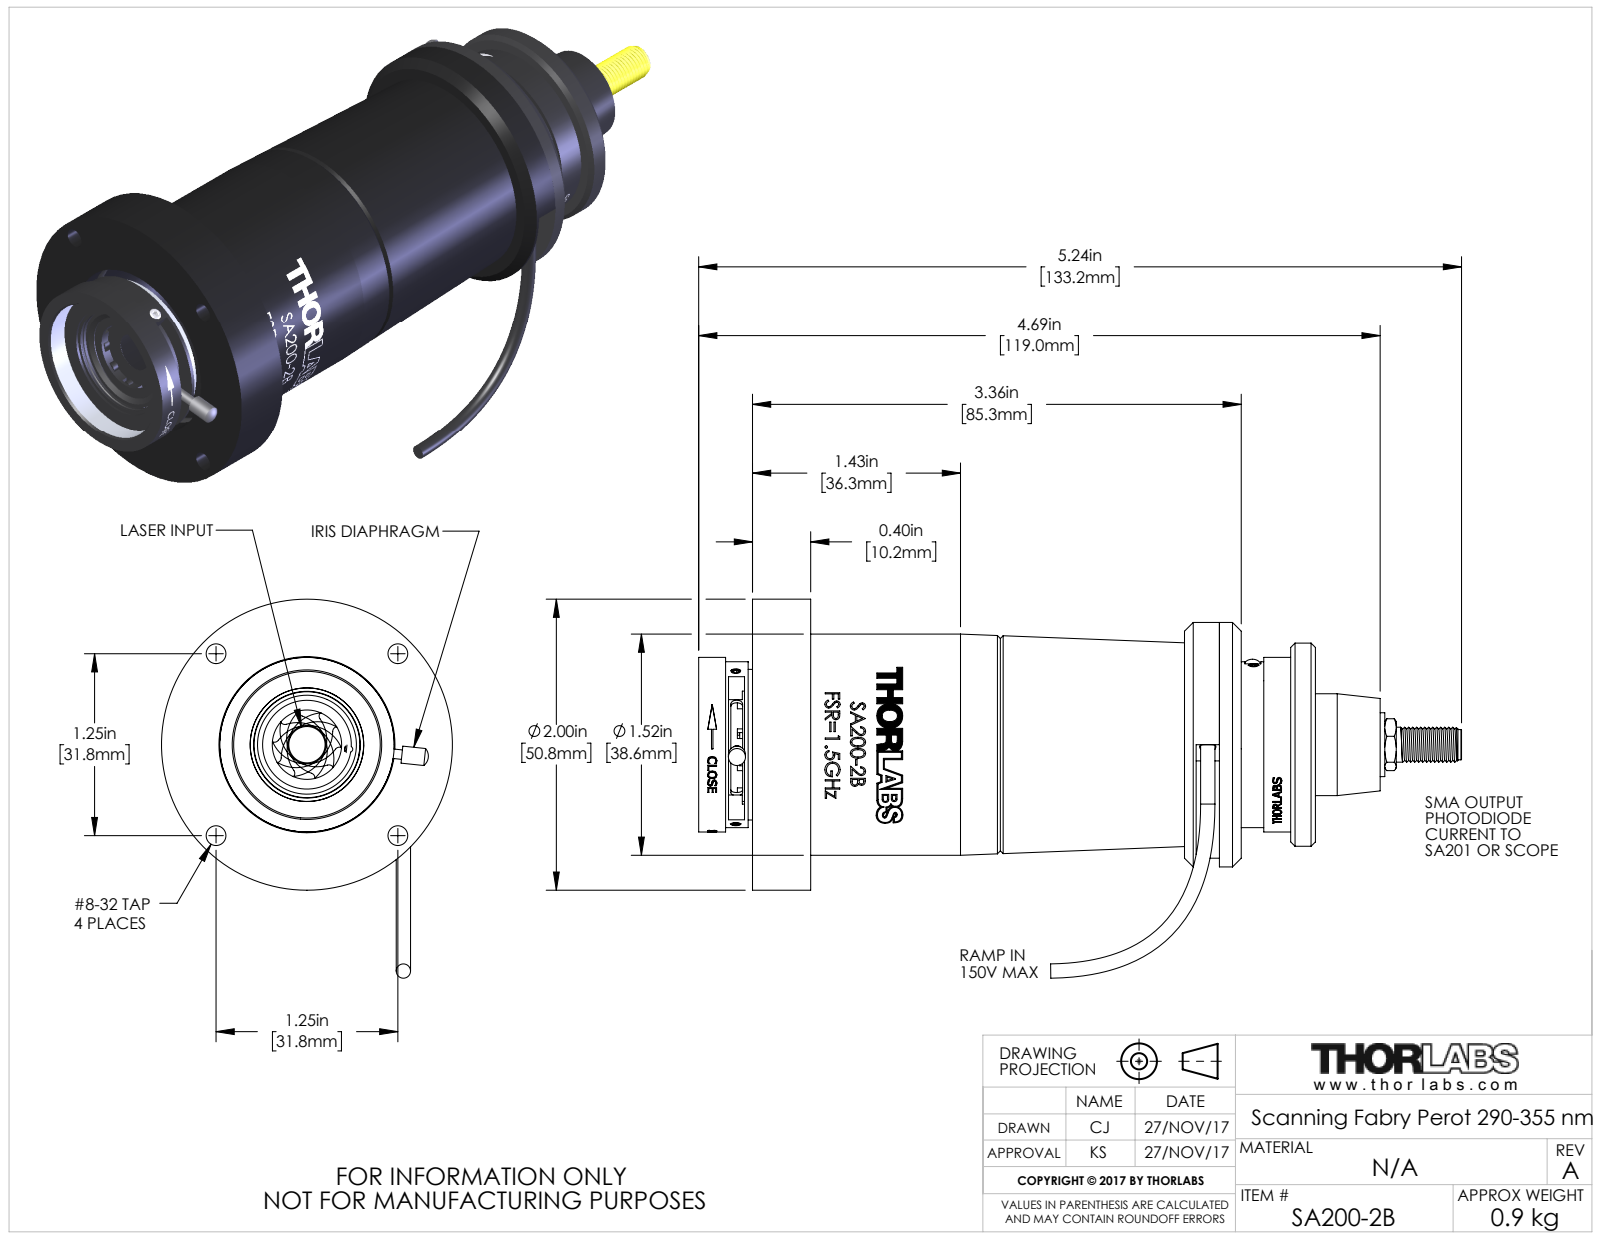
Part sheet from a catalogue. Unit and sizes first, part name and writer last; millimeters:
Units: millimetres
Overall size (bounding box): 133.21 × 66.16 × 50.8
Round holes (diameter × count): ⌀1.68 ×20, ⌀3.45 ×4, ⌀1.1 ×2, ⌀1.6 ×2, ⌀1 ×1, ⌀2.87 ×1, ⌀4.6 ×1, ⌀6.35 ×1, ⌀8.26 ×1, ⌀9.78 ×1, ⌀10.16 ×1, ⌀12.04 ×1
Round bosses / shafts (diameter × count): ⌀1.52 ×20, ⌀1.65 ×12, ⌀1.65 ×10, ⌀2.18 ×4, ⌀2.98 ×2, ⌀1.63 ×2, ⌀50.8 ×1, ⌀42.67 ×1
Partial cylindrical surfaces — rounded edges, fillets, slot ends (radius × count): R0.83 ×20, R0.85 ×20, R1.61 ×20, R6.38 ×20, R9.6 ×20, R0.62 ×2, R3.3 ×2, R25.4 ×2
Main face-to-face distances: 81.53, 86.82, 10.16, 3.81, 71.37, 98.29, 88.13, 16.76, 85.34, 75.18
Hole centre spacings: 14.11, 12, 8.72, 4.58, 14.1, 14.83, 8.71, 7.41
Volume: 54 472 mm³ · Surface area: 45 780 mm²
Bodies: 41 solids, 1312 faces (610 planar, 346 cylindrical, 356 other)
Part name (STEP PRODUCT): STN051087-E0W
STEP written by: SolidWorks 2016 (AUTOMOTIVE_DESIGN)
